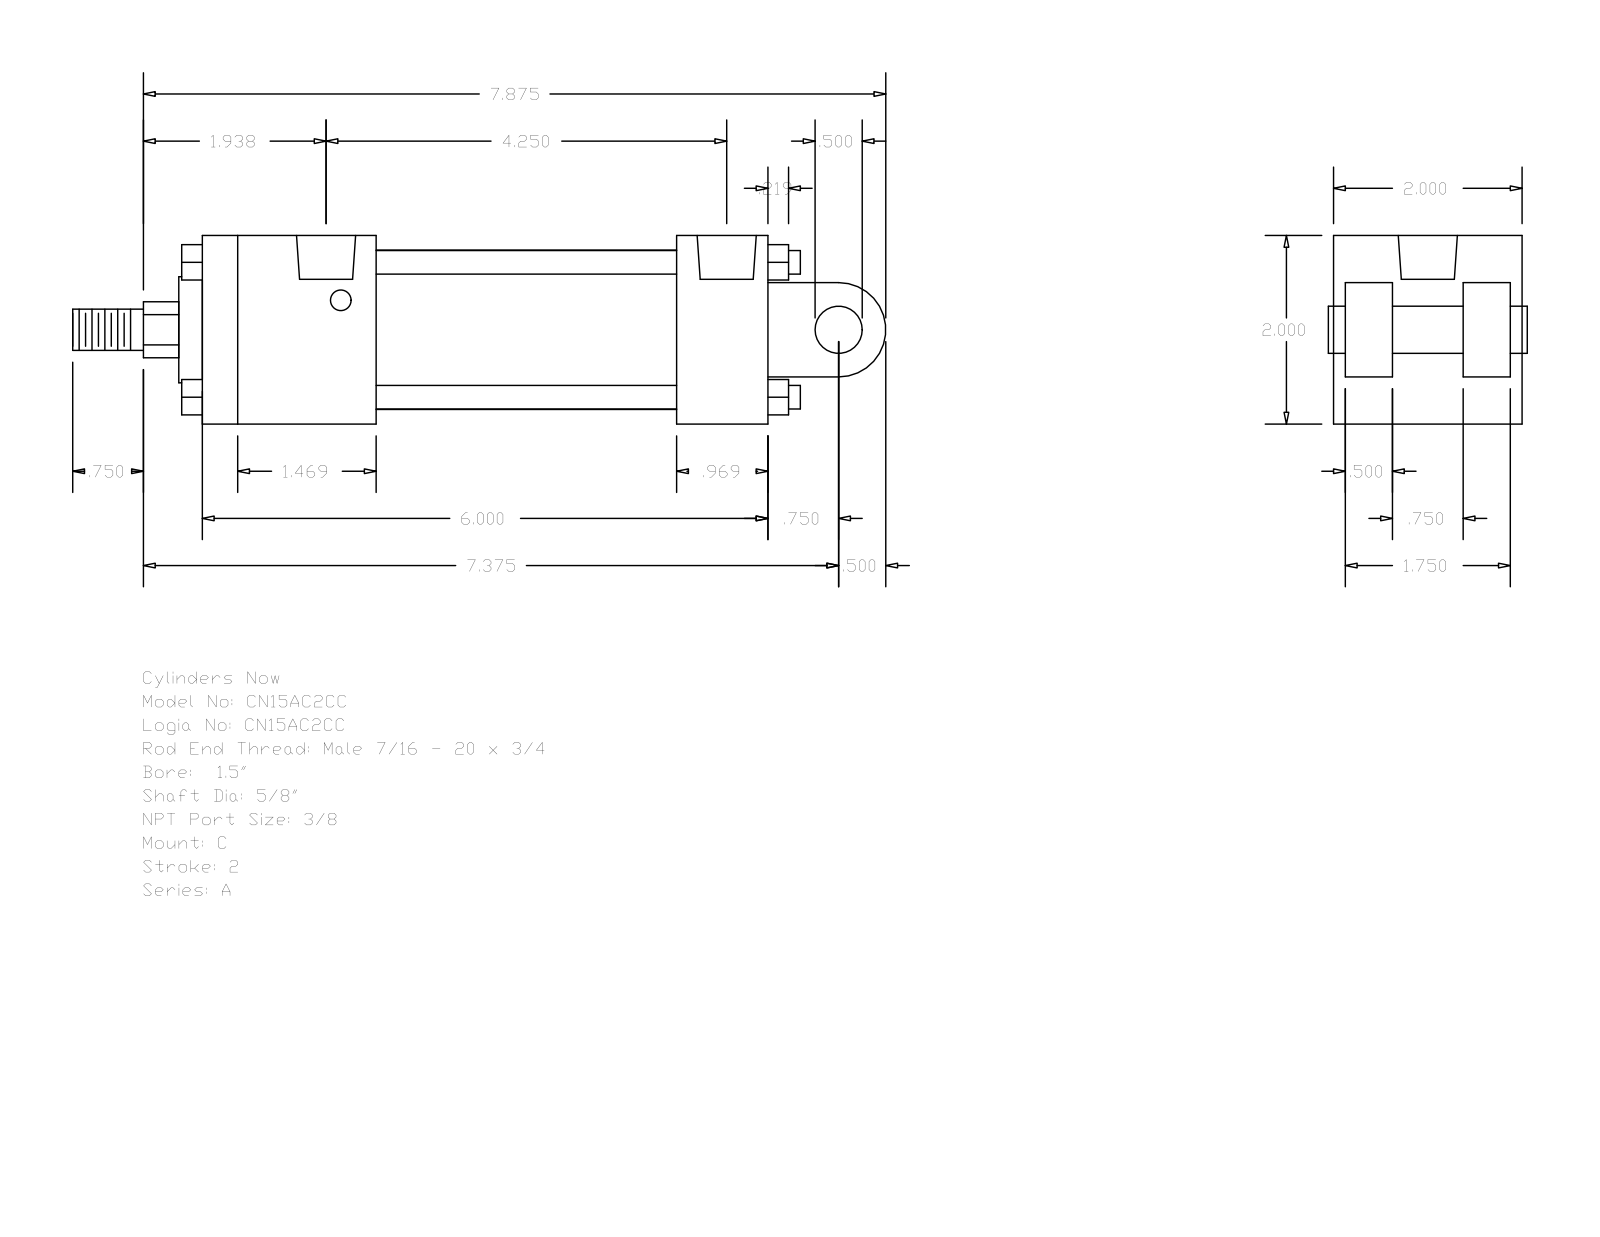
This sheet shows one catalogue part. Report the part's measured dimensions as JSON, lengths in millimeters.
{"part_name": "A_C__0150_0.625", "step_written_by": "GSSL Pune (CONFIG_CONTROL_DESIGN)", "units": "millimeters", "bodies": {"solids": 0, "faces": 135, "planar": 102, "cylindrical": 33, "other": 0}, "overall_size": [219.07, 50.8, 50.8], "round_holes": [[5.56, 4], [15.93, 2]], "round_bosses_or_shafts": [[6.35, 4], [42.93, 1], [28.57, 1], [15.88, 1], [12.7, 1], [11.11, 1]], "partial_cylinders_radius": [[7.54, 1], [12.7, 1]], "face_to_face_distances": [50.8, 12.7, 152.4, 34.93, 3.17, 47.63, 15.87, 31.76, 127.79, 24.61], "hole_center_spacings": [3.97, 100.01, 103.98, 107.95]}
